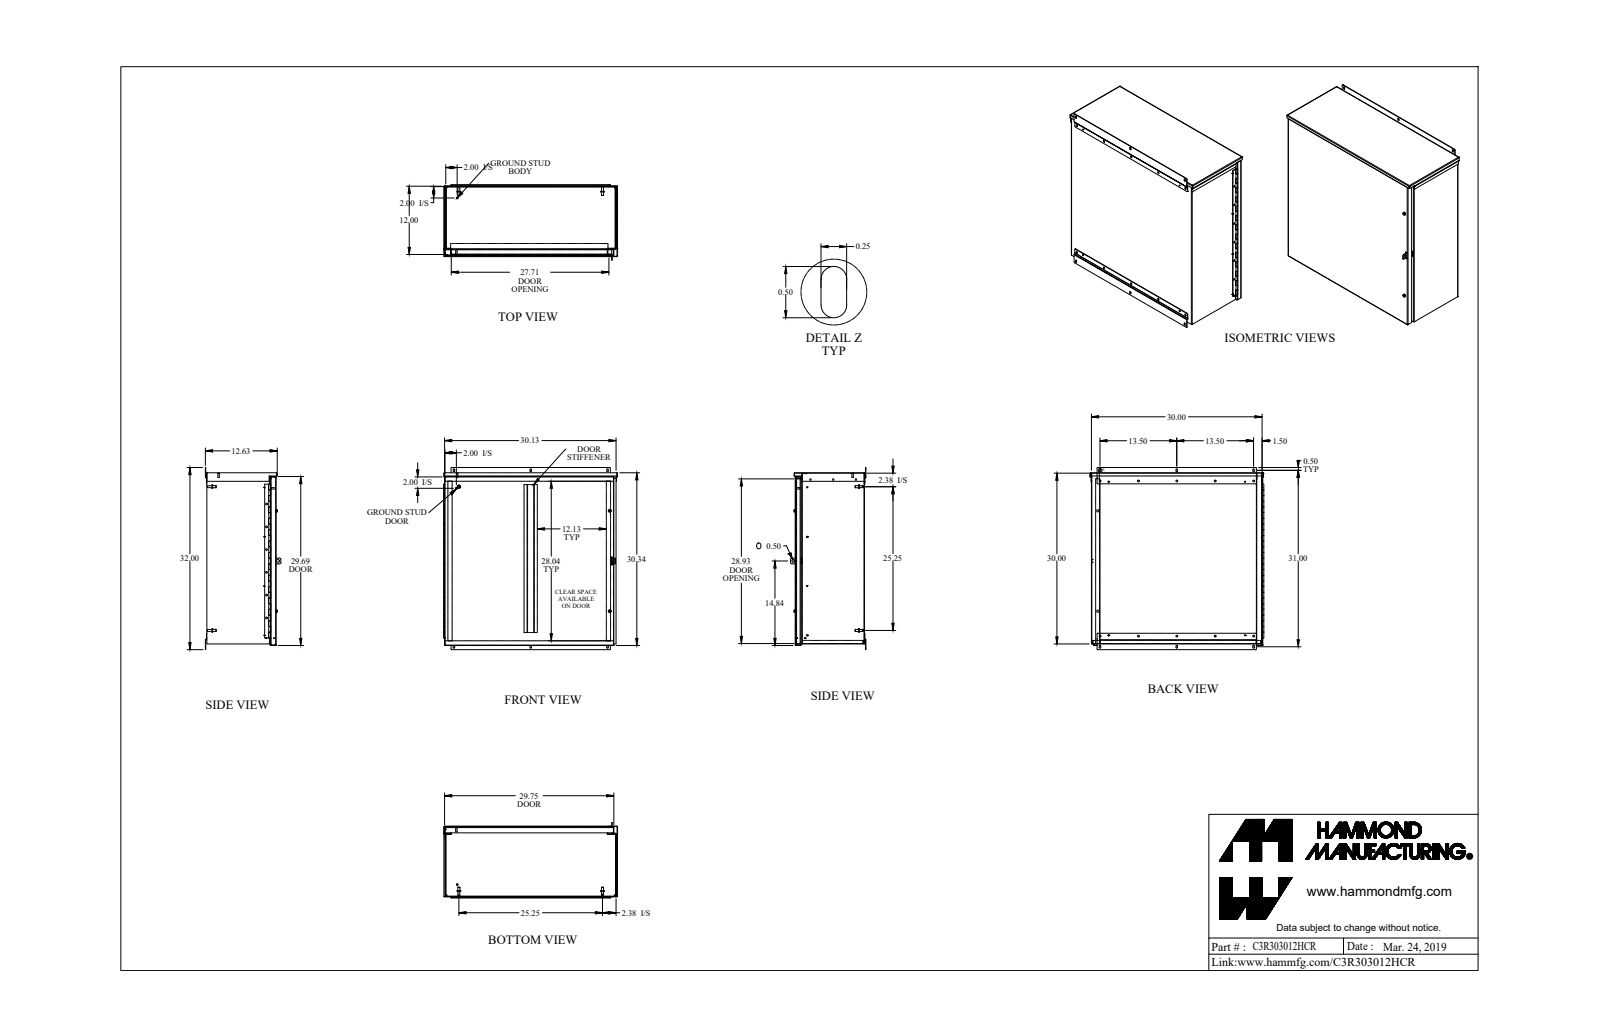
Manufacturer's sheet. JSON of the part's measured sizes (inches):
{"part_name": "C3R303012HCR_Default", "step_written_by": "SolidWorks 2019 (CONFIG_CONTROL_DESIGN)", "units": "inches", "bodies": {"solids": 35, "faces": 1014, "planar": 549, "cylindrical": 411, "other": 54}, "overall_size": [32, 30.571, 13.26], "volume_in3": 305.1, "surface_area_in2": 8317, "round_holes": [[0.312, 10], [0.304, 6], [0.137, 4], [0.14, 4], [0.25, 3], [0.26, 3], [0.313, 3], [0.266, 2], [0.28, 2], [0.29, 2], [0.397, 2], [0.188, 1]], "round_bosses_or_shafts": [[0.131, 10], [0.65, 4], [0.375, 4], [0.33, 4], [0.51, 3], [0.244, 3], [0.187, 3], [0.5, 2]], "partial_cylinders_radius": [[0.036, 39], [0.108, 39], [0.125, 23], [0.171, 3], [0.25, 2]], "face_to_face_distances": [0.072, 12.1, 30, 12.172, 29.928, 12.028, 30.072, 29.856, 0.259, 0.187], "hole_center_spacings": [6.75, 28.074, 4, 13.5, 30.411, 8, 27.25, 1.505]}
